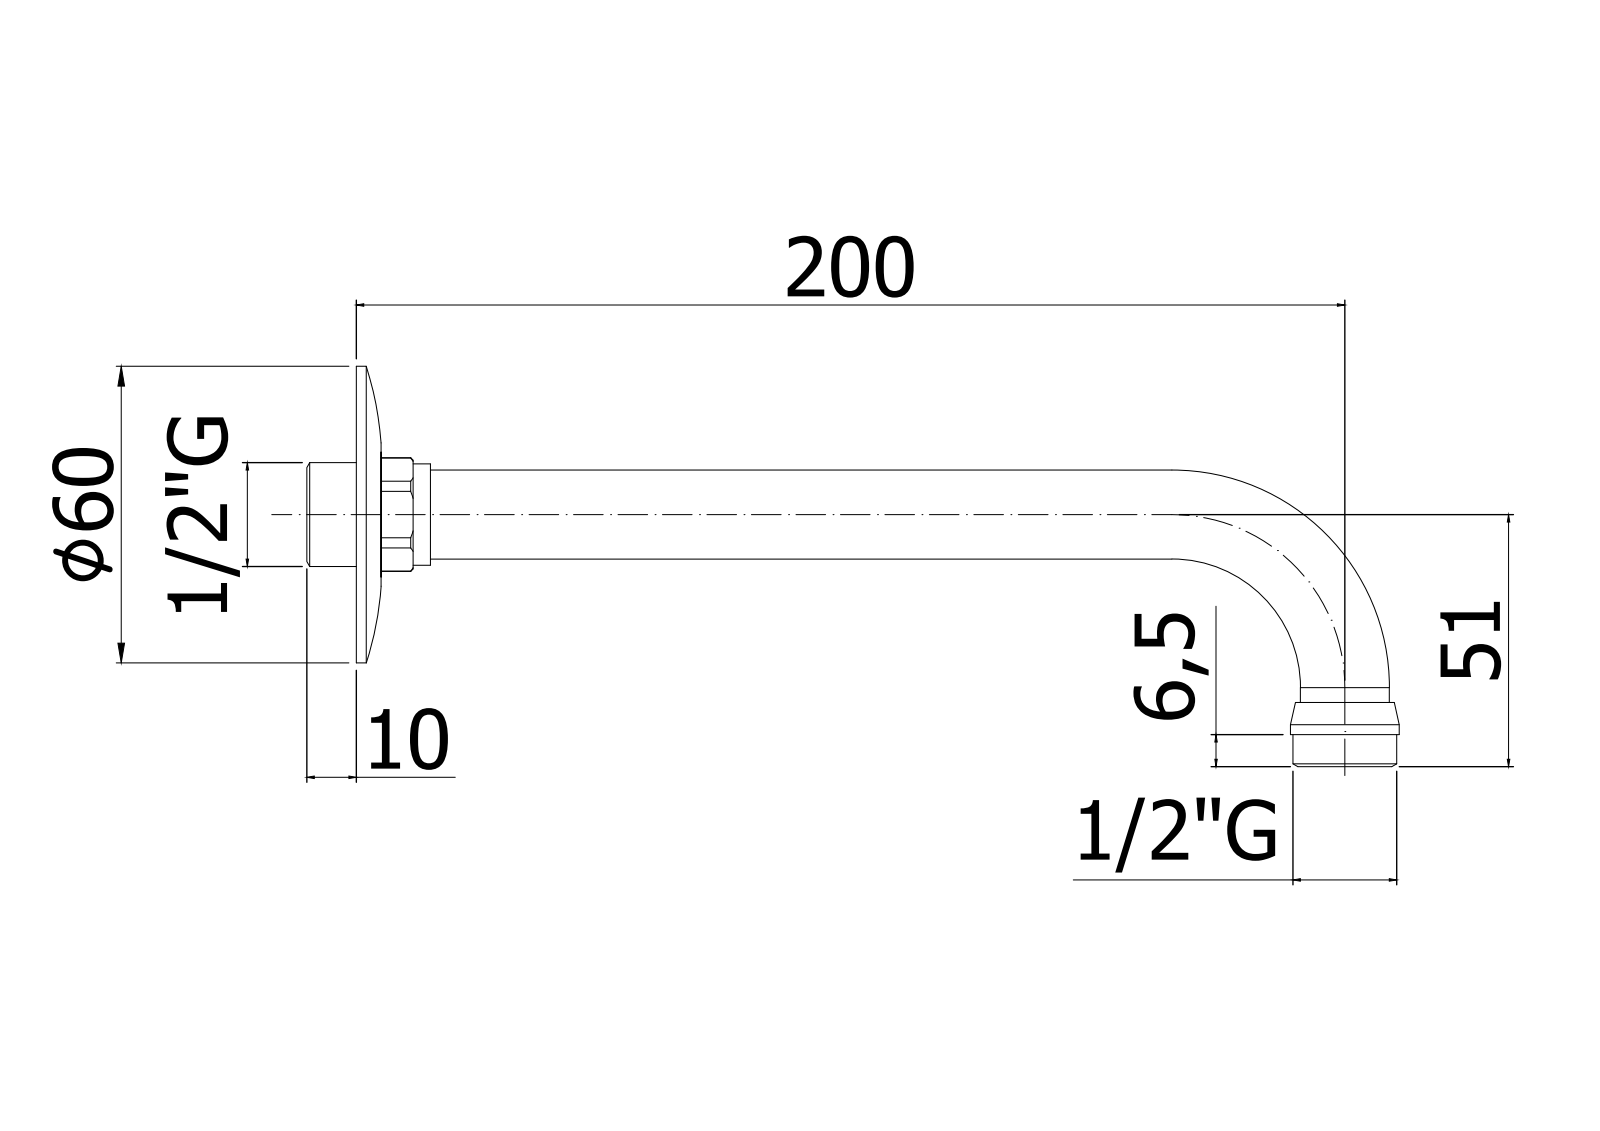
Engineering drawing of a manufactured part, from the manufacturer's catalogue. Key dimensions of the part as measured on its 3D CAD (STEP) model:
Part name (STEP PRODUCT): ZSOF018CR
STEP written by: CREO PARAMETRIC BY PTC INC, 2020044 (CONFIG_CONTROL_DESIGN)
Units: millimetres
Bodies: 1 solid, 88 faces (24 planar, 26 cylindrical, 38 other)
Overall size (bounding box): 211 × 80 × 58
Volume: 12 158 mm³ · Surface area: 32 483 mm²
Round holes (diameter × count): ⌀15 ×2, ⌀17 ×1, ⌀57 ×1
Round bosses / shafts (diameter × count): ⌀21 ×2, ⌀58 ×1, ⌀22 ×1, ⌀18 ×1
Partial cylindrical surfaces — rounded edges, fillets, slot ends (radius × count): R11.5 ×1
Main face-to-face distances: 4, 21, 4.5, 0.5, 15, 11, 10.5, 13, 8, 3.5
